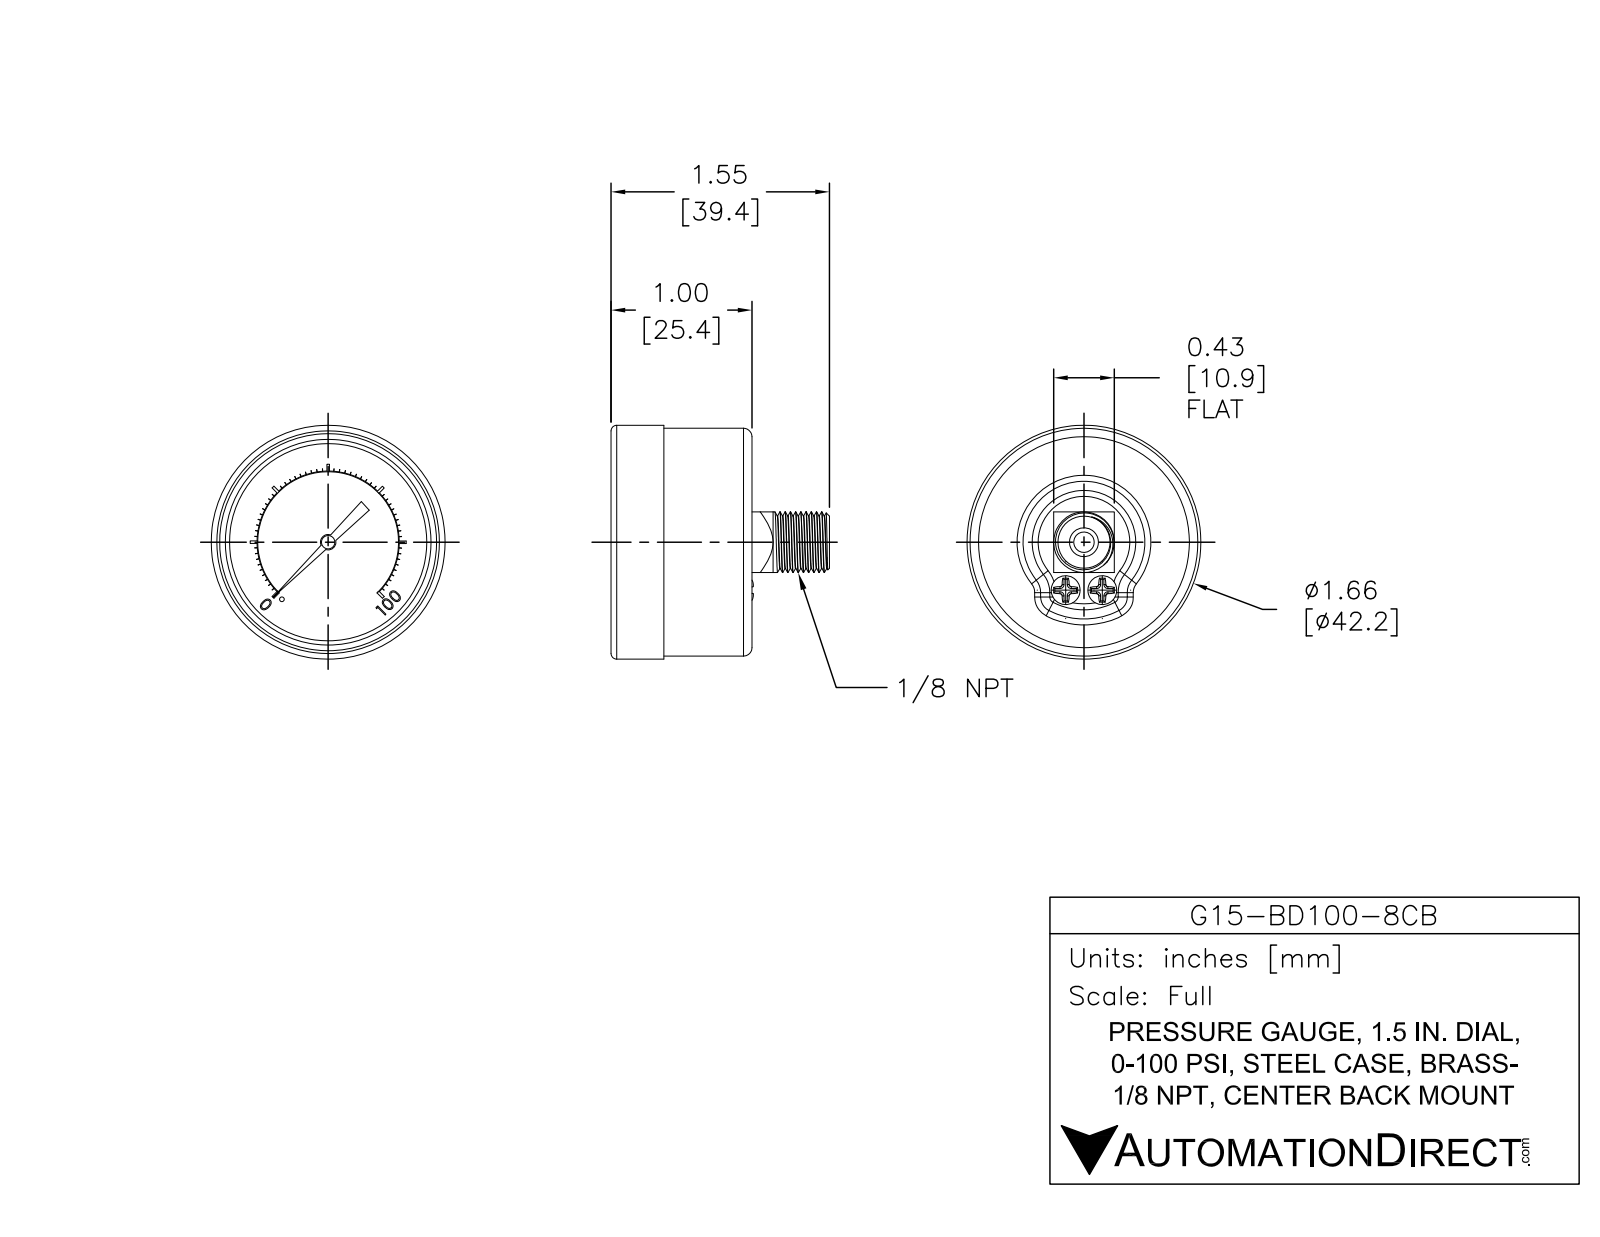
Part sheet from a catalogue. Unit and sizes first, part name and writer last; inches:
Units: inches
Overall size (bounding box): 1.66 × 1.66 × 1.55
Round holes (diameter × count): ⌀0.145 ×1, ⌀1.4 ×1
Round bosses / shafts (diameter × count): ⌀0.205 ×2, ⌀1.66 ×1, ⌀1.617 ×1, ⌀0.43 ×1, ⌀0.086 ×1, ⌀0.06 ×1, ⌀0.033 ×1
Partial cylindrical surfaces — rounded edges, fillets, slot ends (radius × count): R0.06 ×4, R0.015 ×2, R0.048 ×1, R0.5 ×1, R0.505 ×1
Main face-to-face distances: 0.71, 0.43, 0.1, 0.61, 0.96, 0.86, 0.25, 0.04, 0.625, 0.525
Volume: 1.676 in³ · Surface area: 12.02 in²
Bodies: 1 solid, 419 faces (270 planar, 85 cylindrical, 64 other)
Part name (STEP PRODUCT): G15-BD100-8CB
STEP written by: SolidWorks 2021 (AUTOMOTIVE_DESIGN)
